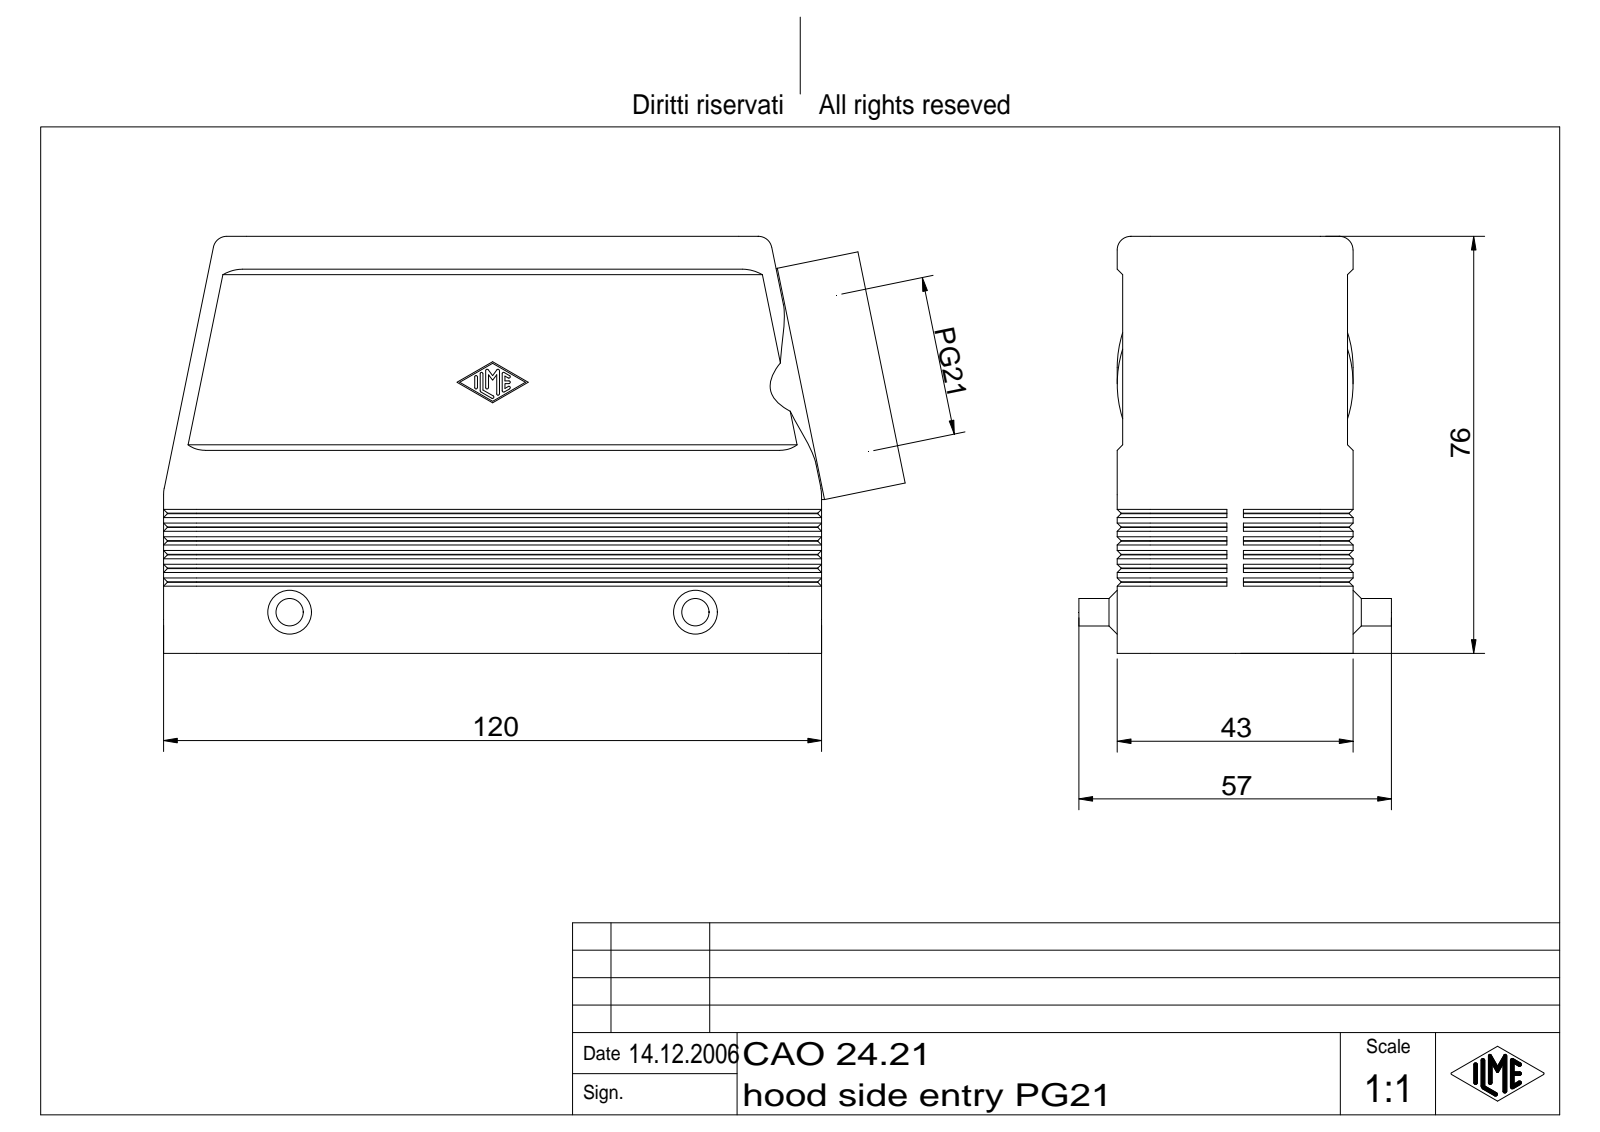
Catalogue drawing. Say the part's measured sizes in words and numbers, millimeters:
The part is named "CAO Tüllengehäuse 2 Bügel für einen Einsatz". Its 3-D file was written by "Autodesk Inventor 7 (AUTOMOTIVE_DESIGN)". It is 1 solid with 526 faces: 192 planar, 134 cylindrical and 200 other. Overall it measures 135.24 by 76 by 57 millimeters. Its volume is 97 634 cubic millimeters and its surface area 57 772 square millimeters. Round holes: 1 of diameter 24.78, 1 of diameter 26.78. Round bosses or shafts: 2 of diameter 5, 1 of diameter 43. Partial cylindrical surfaces (rounded edges, fillets, slot ends): 14 of radius 0.25, 10 of radius 6, 4 of radius 2, 4 of radius 2.5, 4 of radius 3, 2 of radius 5.3. The main face-to-face distances are 3, 37, 40, 2, 39, 1, 42, 43, 41, 1.77.
